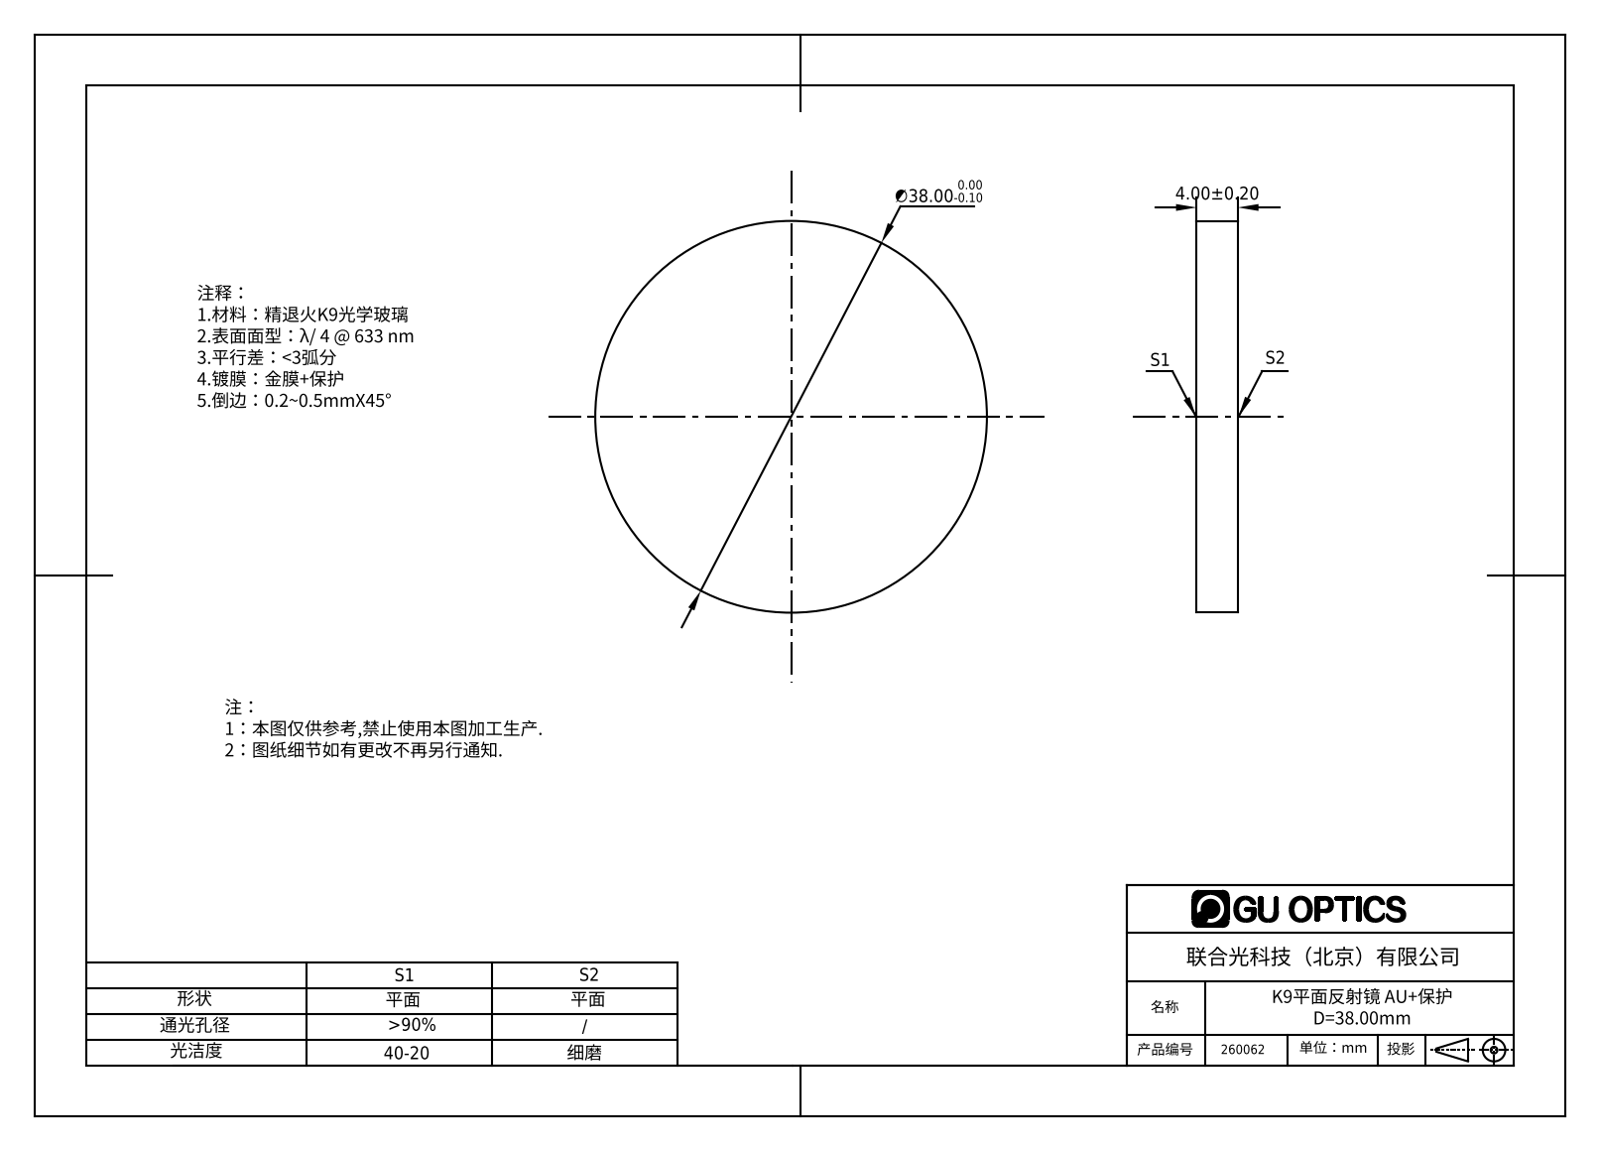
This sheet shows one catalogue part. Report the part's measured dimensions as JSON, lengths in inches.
{"part_name": "260010", "step_written_by": "SolidWorks 2016 (AUTOMOTIVE_DESIGN)", "units": "inches", "bodies": {"solids": 1, "faces": 4, "planar": 2, "cylindrical": 2, "other": 0}, "overall_size": [1.496, 1.496, 0.157], "volume_in3": 0.277, "surface_area_in2": 4.256, "round_bosses_or_shafts": [[1.496, 1]], "face_to_face_distances": [0.157]}
